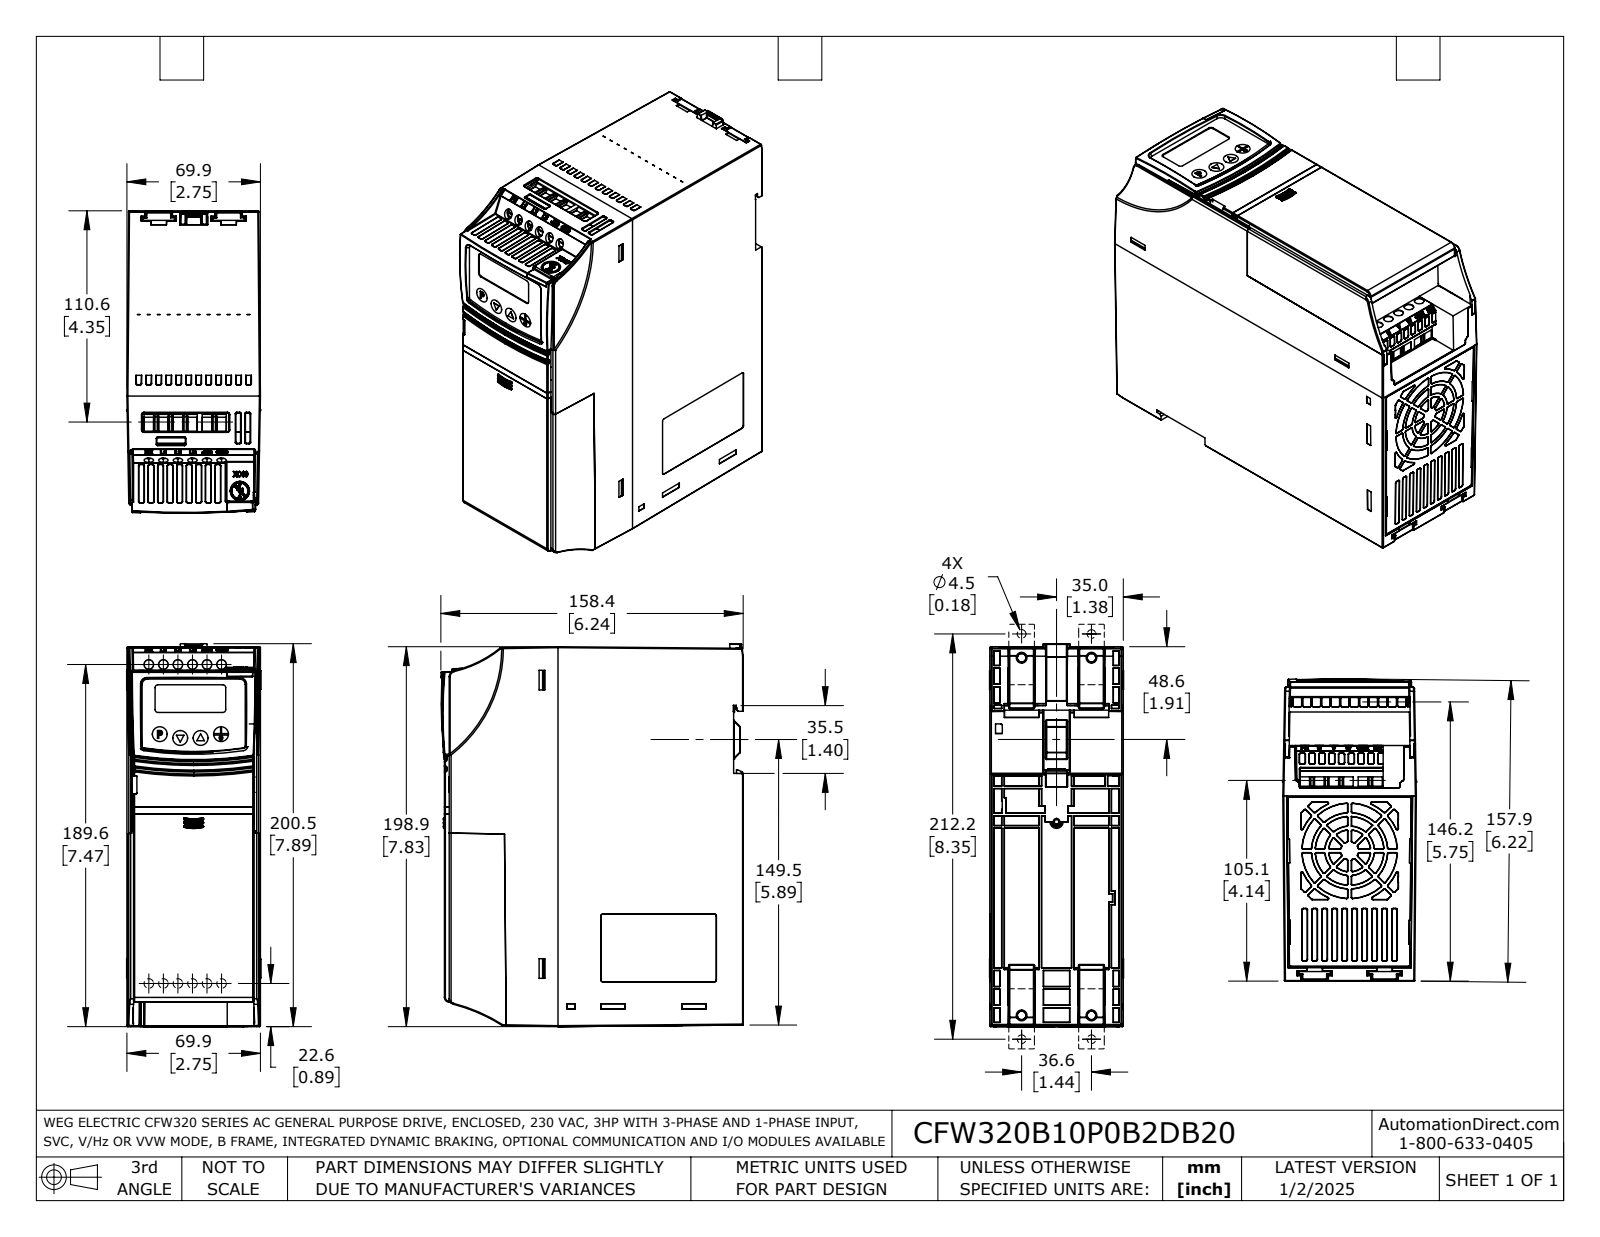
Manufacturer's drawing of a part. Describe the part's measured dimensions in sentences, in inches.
The part is named "CFW320B10P0B2DB20". Its 3-D file was written by "SolidWorks 2021 (AUTOMOTIVE_DESIGN)". It is 5 solids with 3984 faces: 1907 planar, 899 cylindrical and 1178 other. Overall it measures 7.894 by 6.235 by 2.764 inches. Its volume is 24.51 cubic inches and its surface area 385.1 square inches. Round holes: 6 of diameter 0.193. Partial cylindrical surfaces (rounded edges, fillets, slot ends): 355 of radius 0.012, 181 of radius 0.02, 14 of radius 0.039, 7 of radius 0.03, 5 of radius 0.118, 2 of radius 0.01, 2 of radius 0.109, 1 of radius 0.098. The main face-to-face distances are 0.209, 0.098, 0.1, 5.826, 5.728, 0.211, 5.939, 6.037, 7.5, 0.039. The hole center spacings are 0.3, 0.6, 0.9, 1.2, 1.5.
